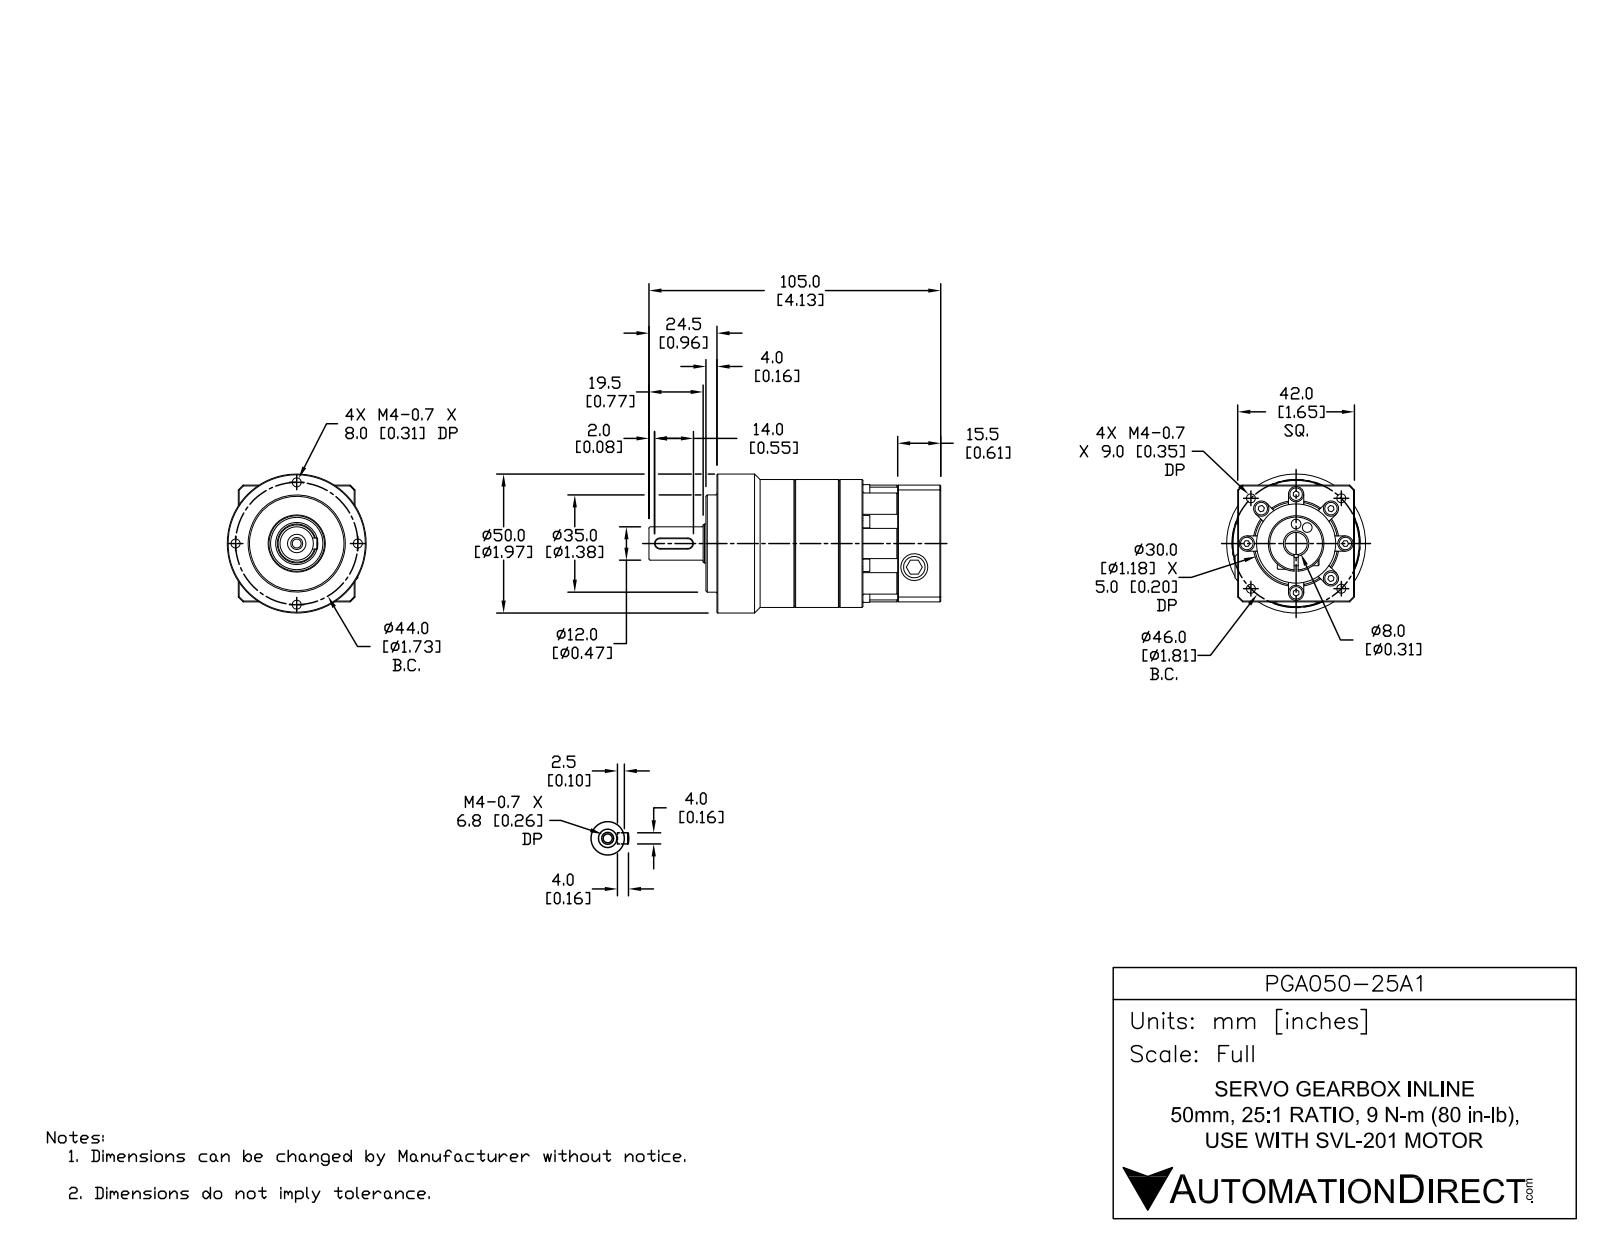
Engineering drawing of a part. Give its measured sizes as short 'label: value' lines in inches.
name: PGA050-25A1
written by: SolidWorks 2014 (AUTOMOTIVE_DESIGN)
unit: in
bodies: 1 solid, 576 faces (229 planar, 161 cylindrical, 186 other)
size: 4.134 × 1.969 × 1.969
volume: 7.909 in³; area: 38.78 in²
holes: 9× ⌀0.128, 7× ⌀0.11, 7× ⌀0.217, 3× ⌀0.138, 1× ⌀0.169, 1× ⌀0.315, 1× ⌀0.787, 1× ⌀1.122
bosses: 15× ⌀0.177, 7× ⌀0.098, 1× ⌀1.969, 1× ⌀1.811, 1× ⌀1.378, 1× ⌀0.551, 1× ⌀0.472, 1× ⌀0.217
rounds: 8× R0.108, 2× R0.079, 1× R0.048, 1× R0.128, 1× R0.157, 1× R0.591, 1× R0.827, 1× R1.122
face distances: 1.654, 2.559, 0.157, 3.169, 0.61, 3.327, 2.717, 0.197, 0.551, 3.13
hole spacings: 0.643, 0.679, 1.113, 1.484, 1.637, 0.699, 0.535, 0.619
